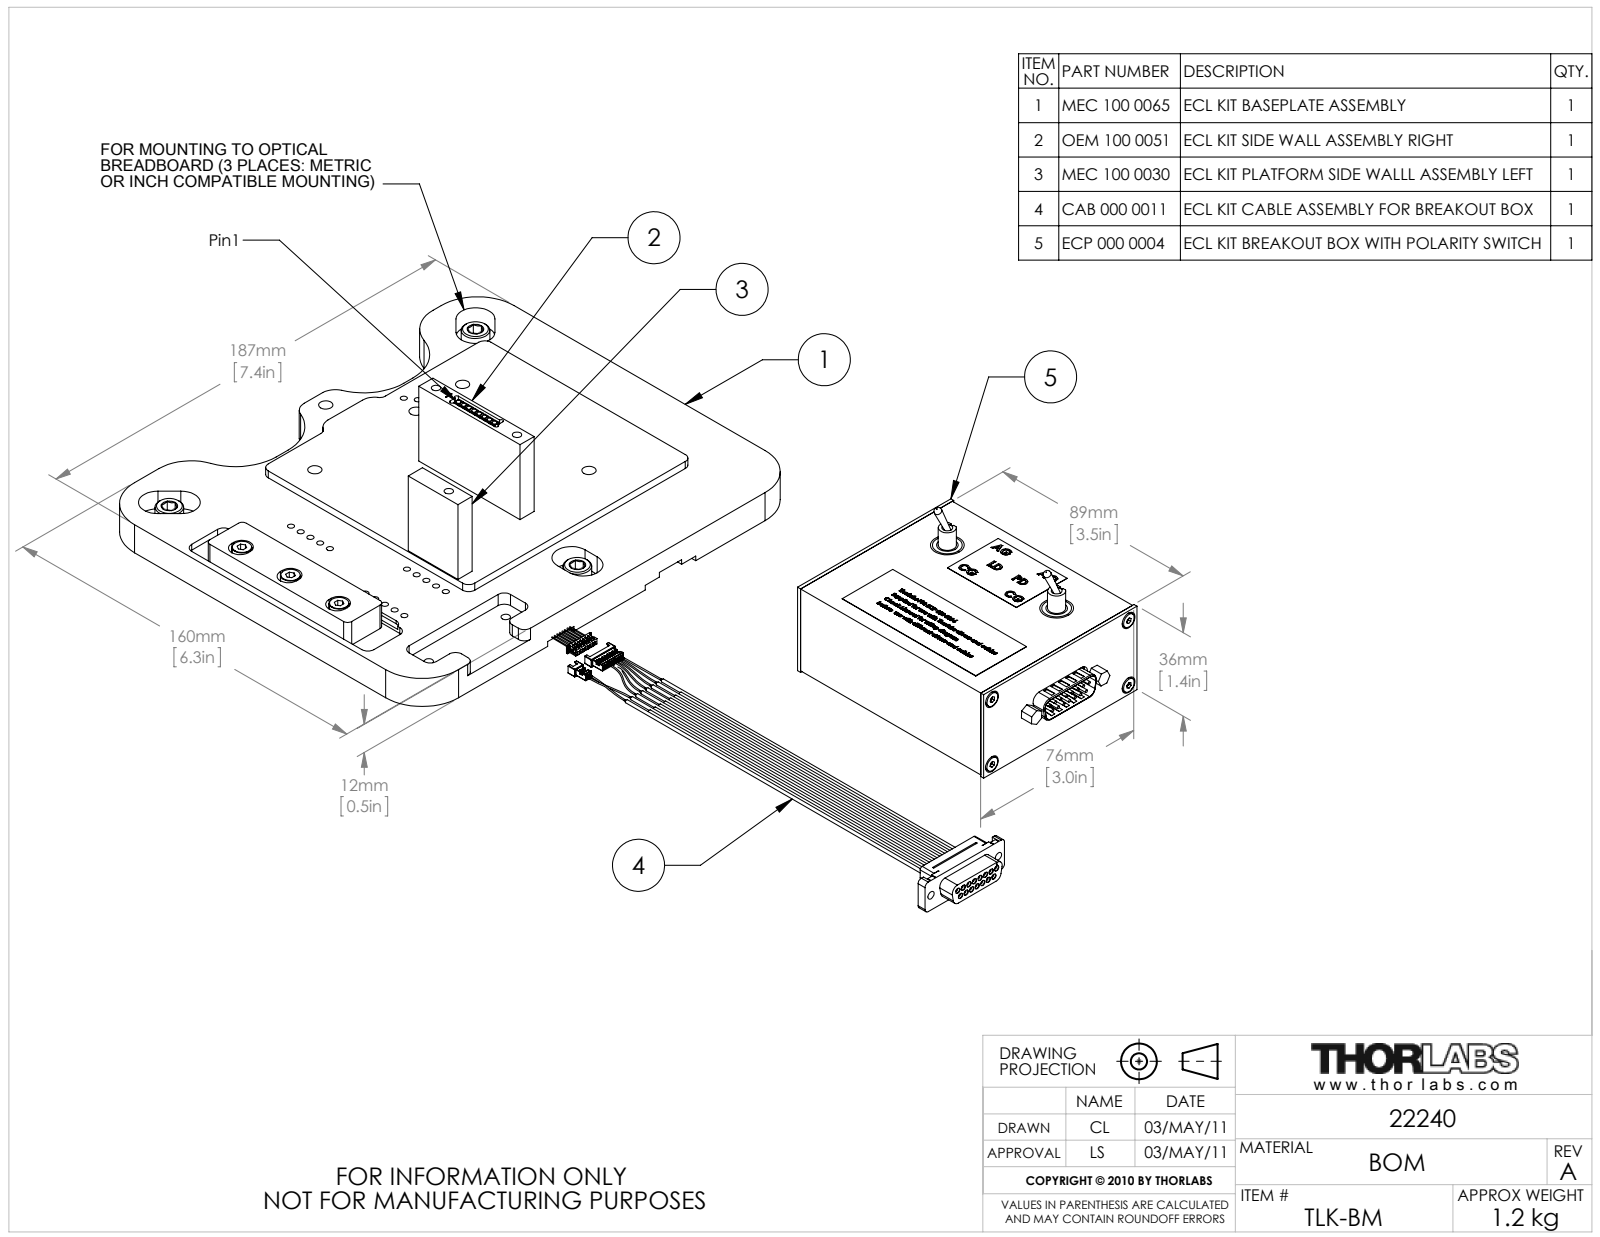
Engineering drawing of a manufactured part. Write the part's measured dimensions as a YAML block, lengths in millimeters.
part_name: "TLK-BM; socket countersunk head screw_am_B18.3.5M - 3 x 0.5 x 6 Socket FCHS -- 6N; Electrical_9-OMA 100 0100 A Enclosure Baseplate Assembly; Cable^Electrical_9-OMA 100 0100 A Enclosure Baseplate Assembly (+8 more)"
step_written_by: "SolidWorks 2011 (CONFIG_CONTROL_DESIGN)"
units: millimeters
bodies: {solids: 123, faces: 8271, planar: 4785, cylindrical: 1756, other: 1730}
overall_size: [370.07, 204.02, 62.05]
volume: 406208
surface_area: 176034
round_holes:
  - {diameter: 2.5, count: 25}
  - {diameter: 1.14, count: 15}
  - {diameter: 2.08, count: 15}
  - {diameter: 3.3, count: 10}
  - {diameter: 1.18, count: 9}
  - {diameter: 2.12, count: 9}
  - {diameter: 2.05, count: 7}
  - {diameter: 3, count: 6}
  - {diameter: 3.4, count: 6}
  - {diameter: 5, count: 5}
  - {diameter: 5.08, count: 5}
  - {diameter: 6.1, count: 5}
round_bosses_or_shafts:
  - {diameter: 0.35, count: 42}
  - {diameter: 0.5, count: 32}
  - {diameter: 1.02, count: 24}
  - {diameter: 0.51, count: 23}
  - {diameter: 1.64, count: 15}
  - {diameter: 1.26, count: 13}
  - {diameter: 0.4, count: 10}
  - {diameter: 0.38, count: 10}
partial_cylinders:
  - {radius: 3, count: 39}
  - {radius: 0.15, count: 33}
  - {radius: 1.57, count: 32}
  - {radius: 0.76, count: 22}
  - {radius: 2, count: 22}
  - {radius: 0.1, count: 21}
  - {radius: 0.17, count: 18}
  - {radius: 0.38, count: 18}
face_to_face_distances: [1.5, 12, 33.5, 15, 3, 20.64, 8.64, 5.64, 26.36, 35]
hole_center_spacings: [3.16, 2.74, 5, 10.01, 8.23, 5.48, 7.43, 10.97]
